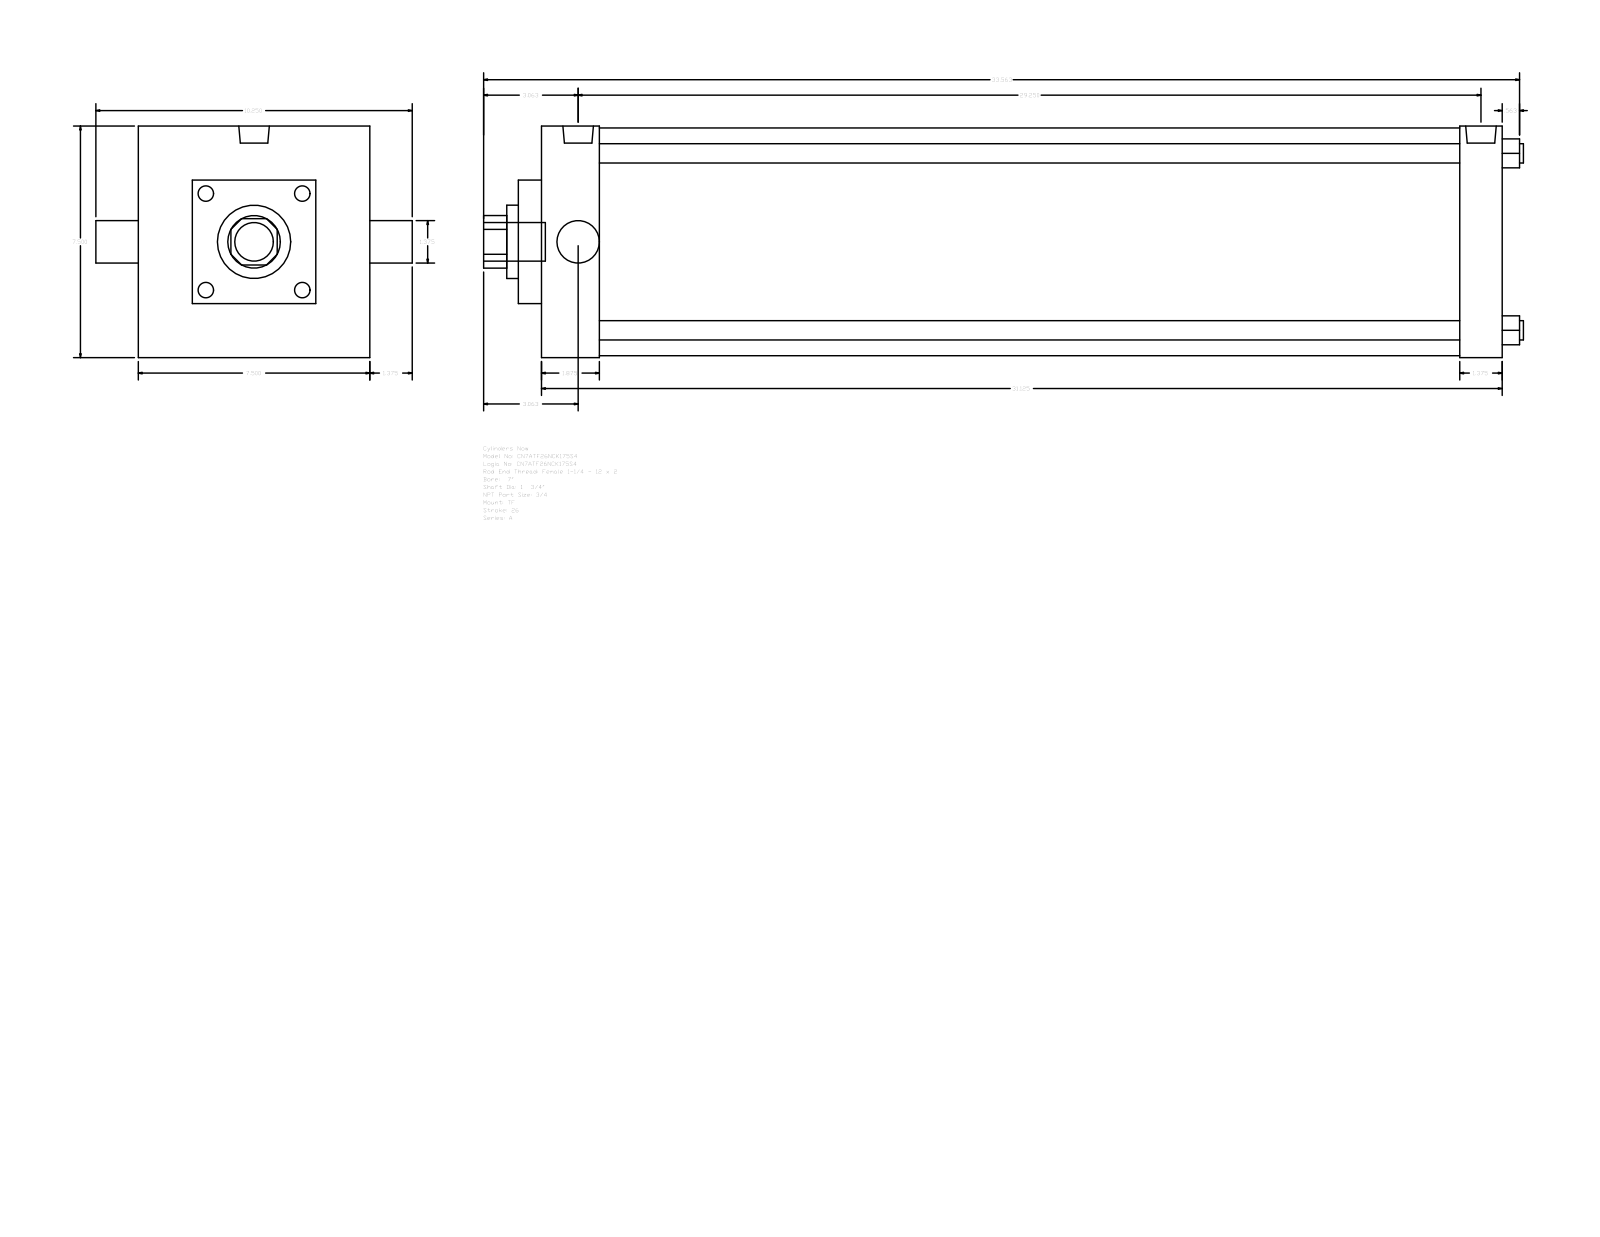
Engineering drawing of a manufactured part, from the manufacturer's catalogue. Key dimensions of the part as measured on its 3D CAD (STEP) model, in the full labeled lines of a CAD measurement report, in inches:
Part name (STEP PRODUCT): A_TF__0700_1.75
STEP written by: GSSL Pune (CONFIG_CONTROL_DESIGN)
Units: inches
Bodies: 0 solids, 89 faces (65 planar, 24 cylindrical, 0 other)
Overall size (bounding box): 33.687 × 10.25 × 7.5
Round holes (diameter × count): ⌀0.625 ×4, ⌀1.375 ×1, ⌀1.75 ×1, ⌀2.375 ×1, ⌀7.375 ×1
Round bosses / shafts (diameter × count): ⌀0.594 ×3, ⌀0.989 ×2, ⌀1.25 ×1
Partial cylindrical surfaces — rounded edges, fillets, slot ends (radius × count): R0.852 ×1
Main face-to-face distances: 7.5, 31.125, 1.375, 1.75, 0.75, 1.875, 29.25, 29.75, 27.875, 5.75
Hole centre spacings: 4.052, 5.73, 8.103
